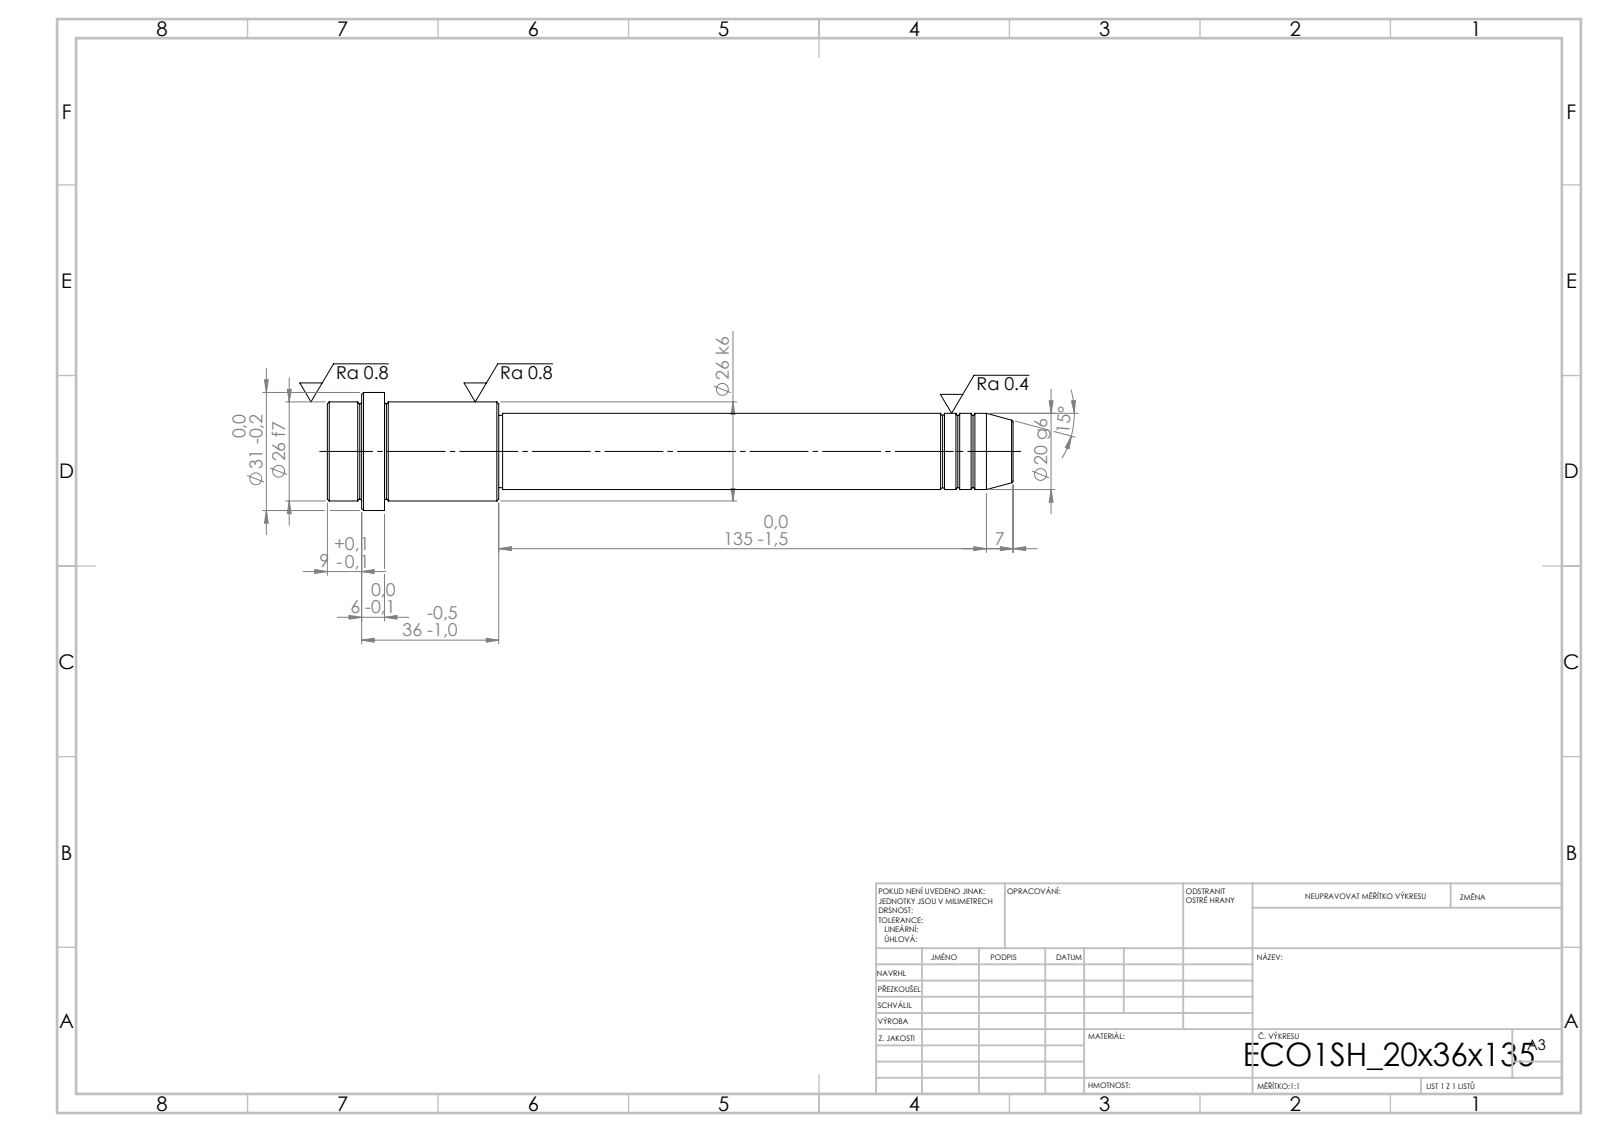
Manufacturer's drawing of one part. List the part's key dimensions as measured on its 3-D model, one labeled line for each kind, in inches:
STEP written by: SolidWorks 2019 (CONFIG_CONTROL_DESIGN)
Units: inches
Bodies: 1 solid, 52 faces (6 planar, 16 cylindrical, 30 other)
Overall size (bounding box): 7.087 × 1.22 × 1.22
Volume: 4.092 in³ · Surface area: 21.37 in²
Round bosses / shafts (diameter × count): ⌀1.22 ×1, ⌀1.024 ×1, ⌀0.787 ×1, ⌀0.748 ×1
Main face-to-face distances: 0.591, 1.181, 1.772, 5.315, 6.496, 7.087, 6.732, 1.417, 0.236, 0.354
